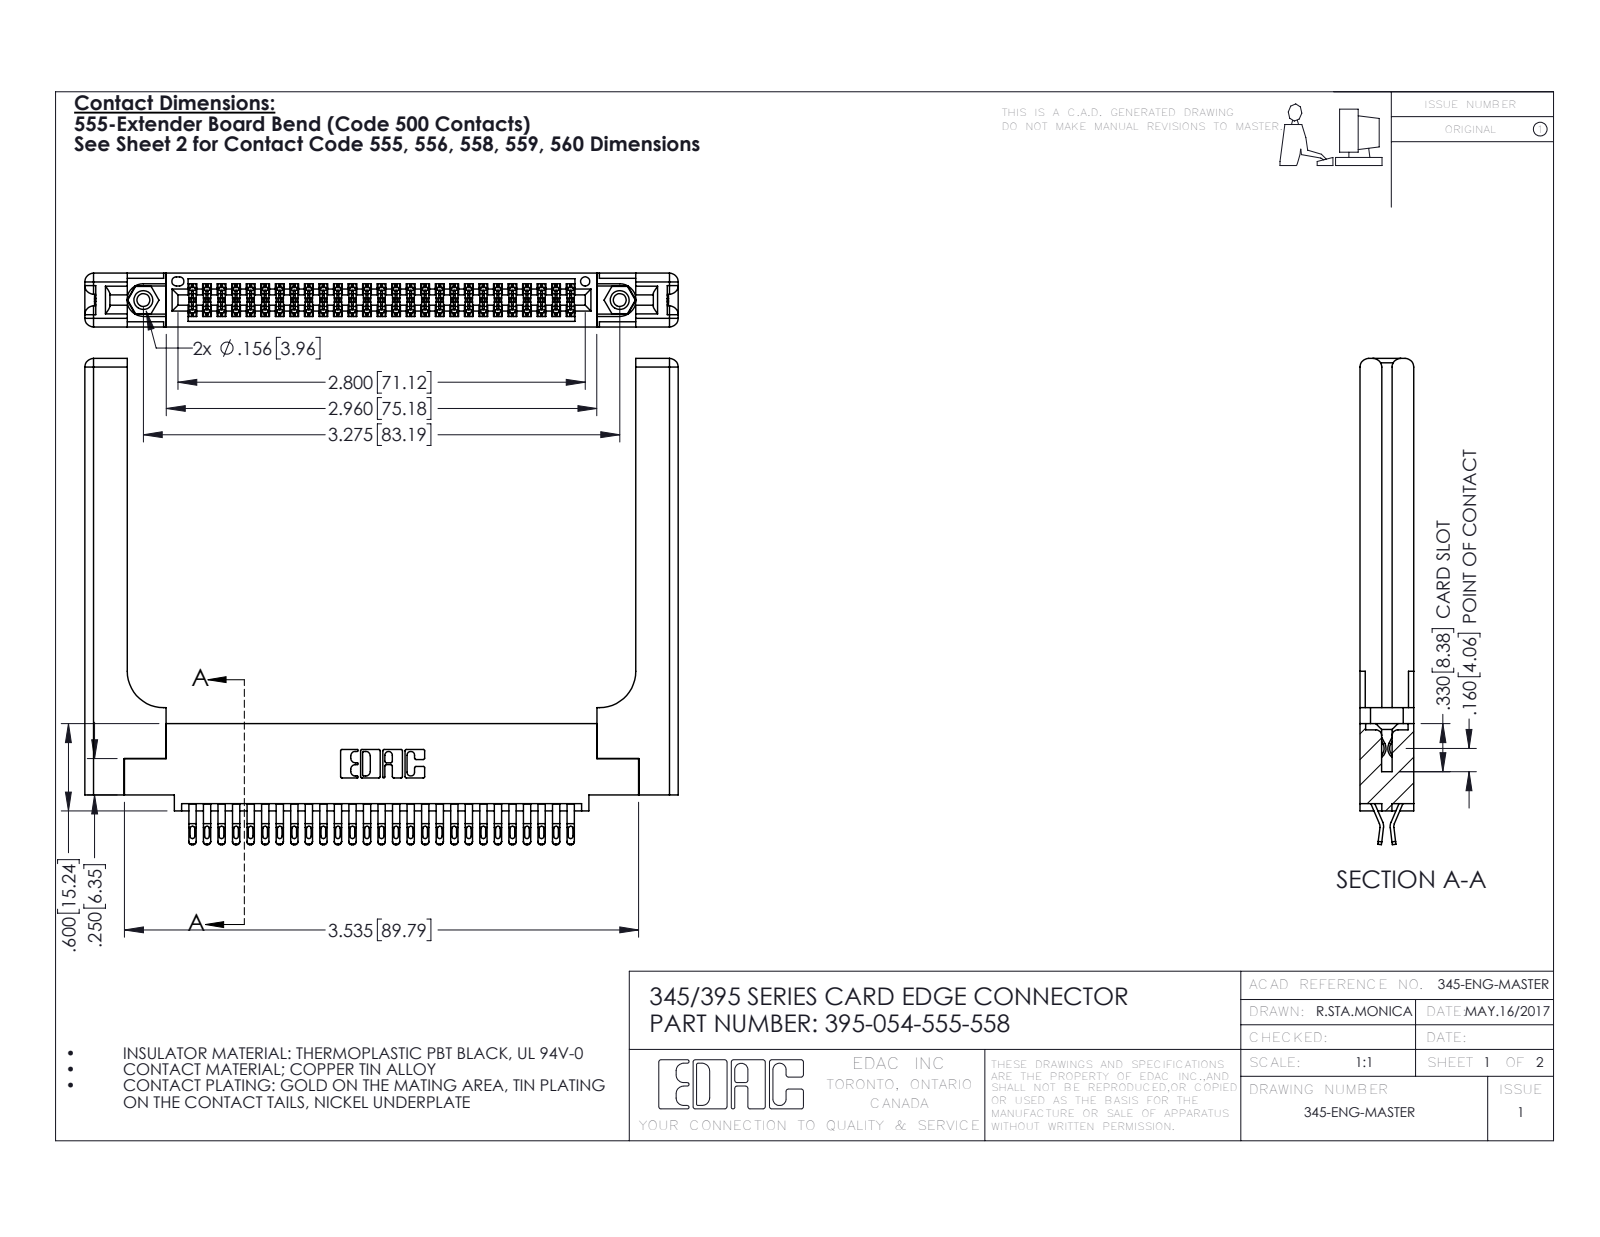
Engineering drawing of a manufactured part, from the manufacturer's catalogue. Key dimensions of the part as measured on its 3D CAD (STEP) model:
Part name (STEP PRODUCT): 395-054-555-558; 345-250-001_345-250-001-102; 345-292-001_555 Tail; 345 Part_0.110 Offset - 0.156 Dia-TH (+1 more)
STEP written by: SolidWorks 2016 (CONFIG_CONTROL_DESIGN)
Units: inches
Bodies: 59 solids, 3410 faces (1906 planar, 1444 cylindrical, 60 other)
Overall size (bounding box): 4.079 × 3.342 × 0.37
Volume: 1.128 in³ · Surface area: 31.31 in²
Round holes (diameter × count): ⌀0.089 ×2, ⌀0.125 ×2, ⌀0.156 ×2, ⌀0.064 ×1
Round bosses / shafts (diameter × count): ⌀0.155 ×2
Partial cylindrical surfaces — rounded edges, fillets, slot ends (radius × count): R0.016 ×135, R0.02 ×108, R0.006 ×81, R0.01 ×22, R0.06 ×16, R0.007 ×6, R0.031 ×6, R0.026 ×3
Main face-to-face distances: 0.37, 0.072, 0.298, 0.025, 0.225, 0.148, 0.15, 0.098, 0.272, 0.2
Hole centre spacings: 0.27, 3.04, 3.275
